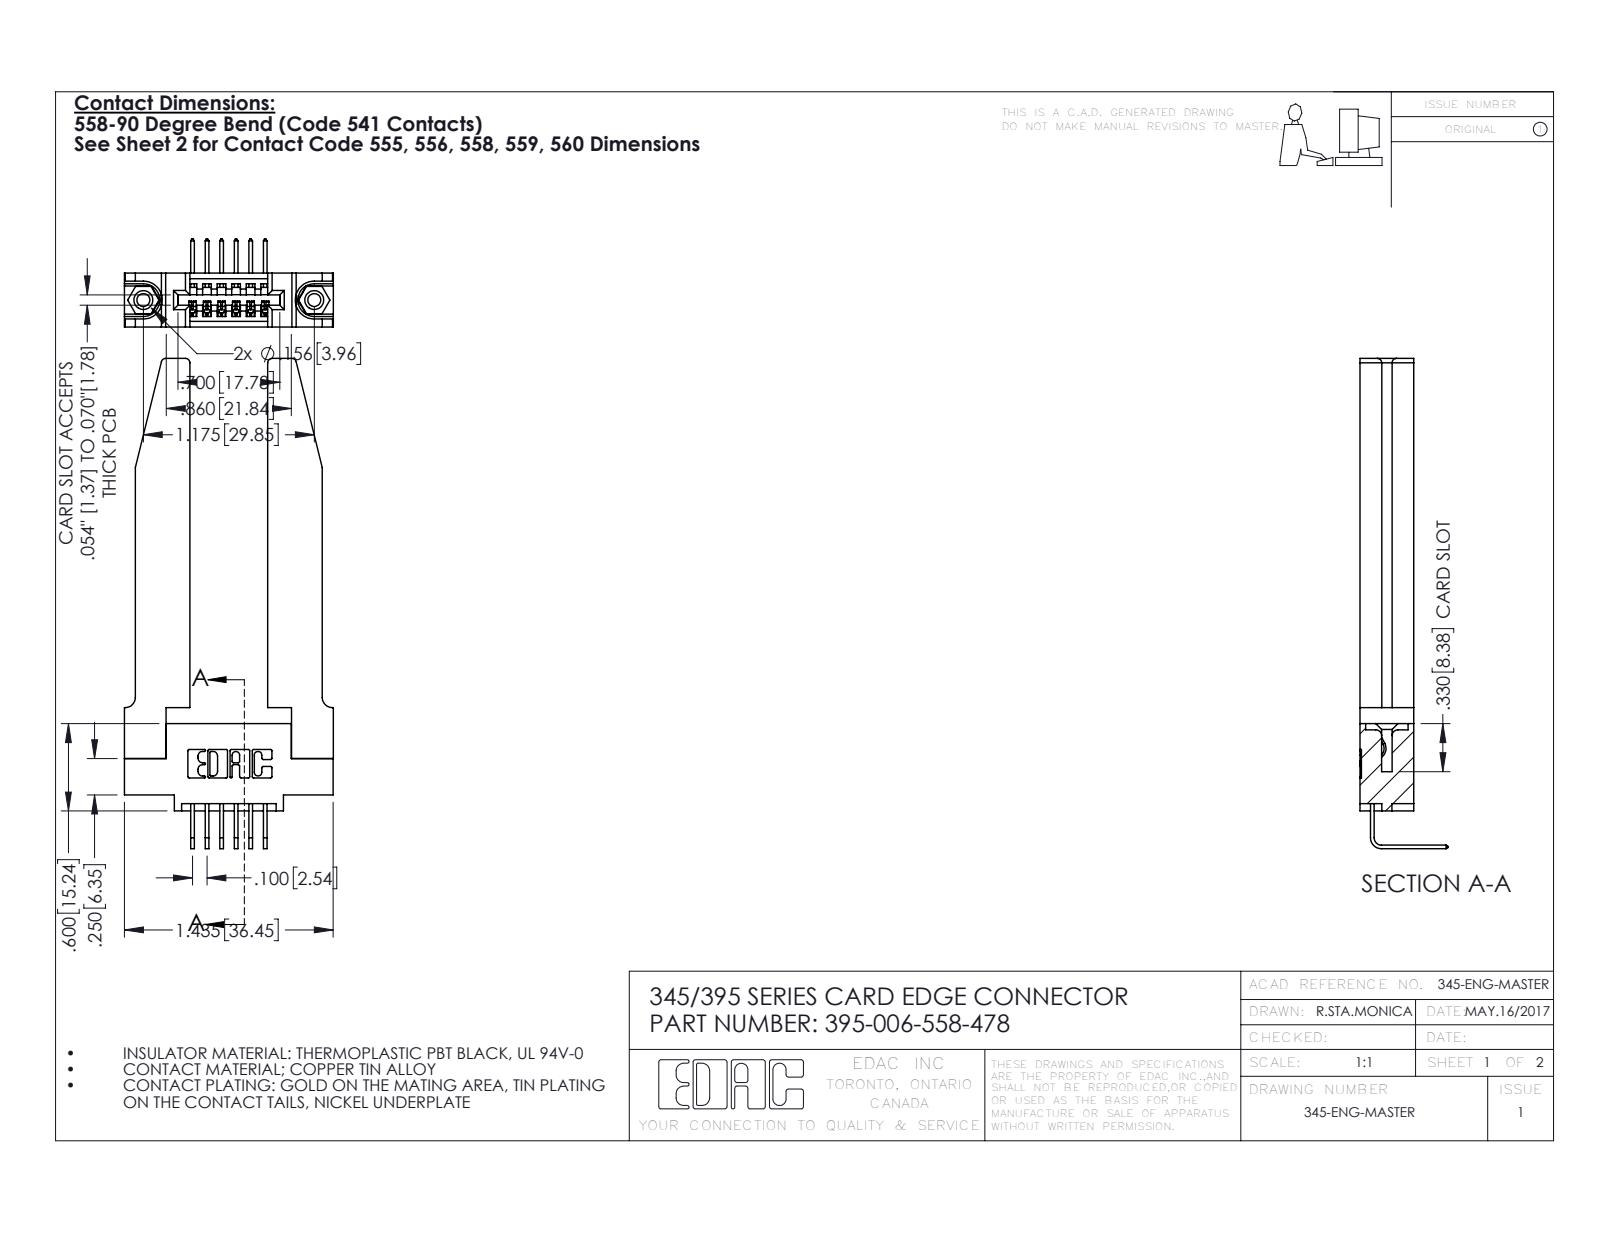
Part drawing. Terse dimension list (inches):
name: 345-250-001_345-250-001-102; 395-006-558-478; 345 Part_0.110 Offset - 0.156 Dia-TH; 345-220-078_345-220-078 (+1 more)
written by: SolidWorks 2016 (CONFIG_CONTROL_DESIGN)
unit: in
bodies: 11 solids, 724 faces (478 planar, 194 cylindrical, 52 other)
size: 3.369 × 1.436 × 0.605
volume: 0.664 in³; area: 16.58 in²
holes: 2× ⌀0.089, 2× ⌀0.125, 2× ⌀0.156, 1× ⌀0.064
bosses: 2× ⌀0.155
rounds: 22× R0.01, 12× R0.006, 8× R0.03, 6× R0.007, 6× R0.031, 3× R0.026, 2× R0.031, 2× R0.04
face distances: 0.37, 0.15, 0.22, 0.535, 0.072, 0.148, 0.298, 0.077, 0.071, 0.055
hole spacings: 0.27, 0.946, 1.175
